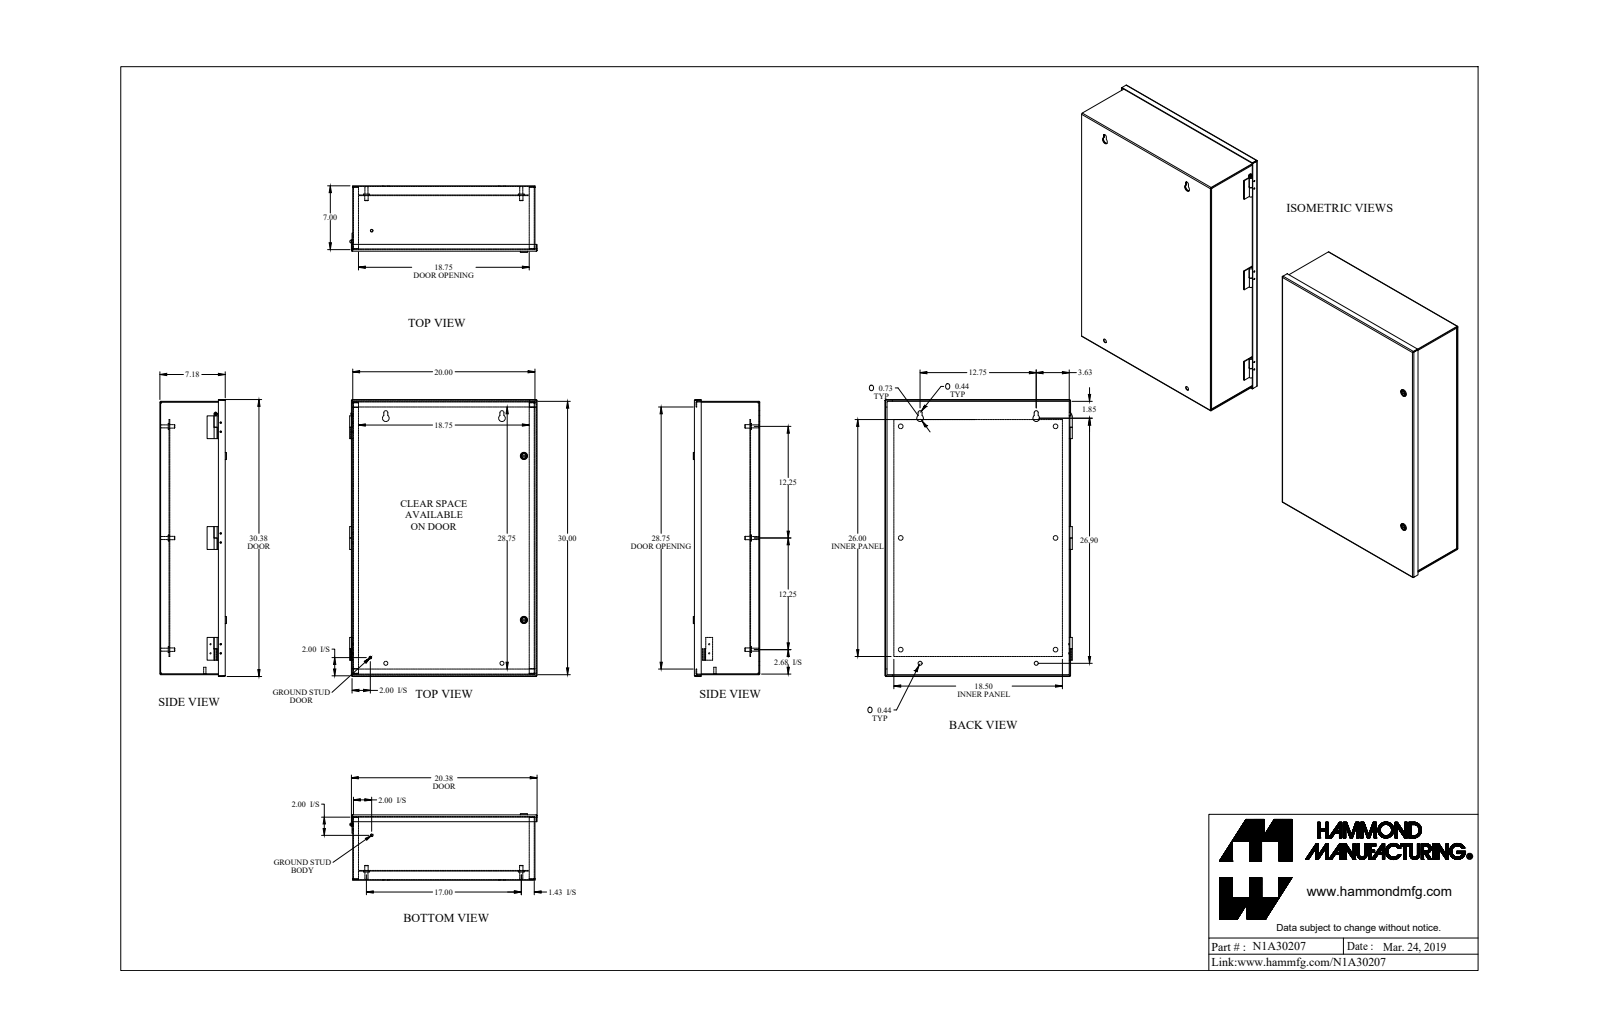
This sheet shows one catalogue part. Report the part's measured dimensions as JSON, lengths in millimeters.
{"part_name": "N1A30207", "step_written_by": "SolidWorks 2018 (AUTOMOTIVE_DESIGN)", "units": "millimeters", "bodies": {"solids": 34, "faces": 767, "planar": 434, "cylindrical": 269, "other": 64}, "overall_size": [771.8, 522.6, 185.4], "volume_mm3": 3079000, "surface_area_mm2": 3374000, "round_holes": [[3.6, 12], [12.7, 6], [7.8, 4], [11.3, 4], [18.6, 4], [11.1, 2], [13.1, 2], [4.3, 1], [4.7, 1]], "round_bosses_or_shafts": [[3.3, 12], [9.5, 7], [16.5, 6], [8.4, 6], [25.4, 4], [20, 2], [13.6, 2], [12.6, 2]], "partial_cylinders_radius": [[0.9, 16], [2.7, 16], [5.6, 3], [1.5, 2], [3.2, 2], [3.9, 2], [8, 2], [0.8, 1]], "face_to_face_distances": [1.8, 180.5, 25.6, 154.8, 178.6, 182.3, 23.8, 27.5, 153, 156.7], "hole_center_spacings": [25.4, 28.4, 308.8, 308.8, 310.1, 310.1, 311.2, 338.3]}
